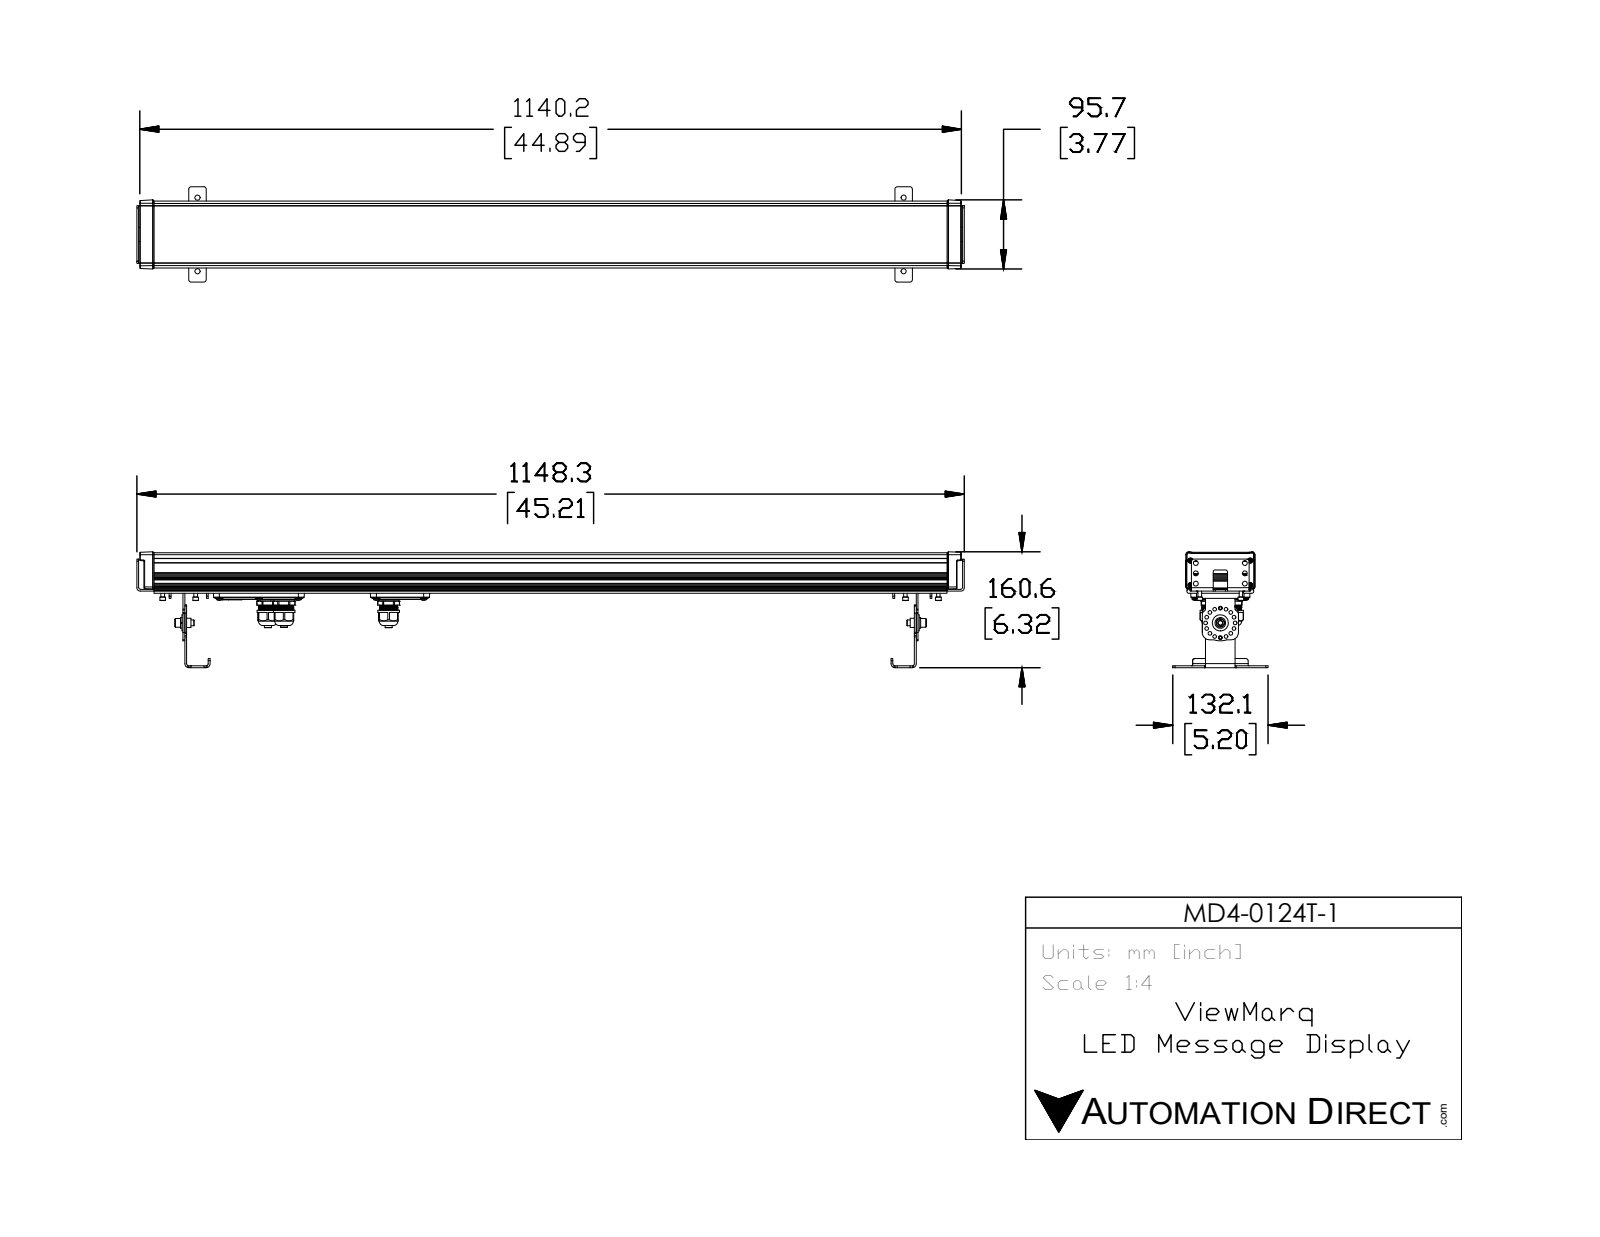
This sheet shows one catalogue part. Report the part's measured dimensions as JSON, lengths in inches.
{"part_name": "MD4-0124T-1", "step_written_by": "SolidWorks 2021 (AUTOMOTIVE_DESIGN)", "units": "inches", "bodies": {"solids": 79, "faces": 5948, "planar": 1735, "cylindrical": 1983, "other": 2230}, "overall_size": [45.21, 6.325, 5.2], "volume_in3": 83.69, "surface_area_in2": 1649, "round_holes": [[0.201, 24], [0.266, 12], [0.281, 12], [0.136, 10], [0.138, 10], [0.165, 10], [0.186, 10], [0.19, 6], [0.144, 4], [0.159, 4], [0.533, 3], [0.602, 3]], "round_bosses_or_shafts": [[0.323, 10], [0.315, 10], [0.159, 10], [0.118, 10], [0.313, 9], [0.22, 4], [0.19, 4], [0.091, 4]], "partial_cylinders_radius": [[0.02, 388], [0.02, 182], [0.01, 142], [0.118, 60], [0.031, 42], [0.039, 42], [0.01, 38], [0.025, 36]], "face_to_face_distances": [0.118, 0.079, 1.736, 1.815, 1.618, 1.696, 0.236, 0.098, 3.657, 1.854], "hole_center_spacings": [0.315, 1.342, 1.491, 0.807, 1.141, 0.618, 0.897, 1.583]}
